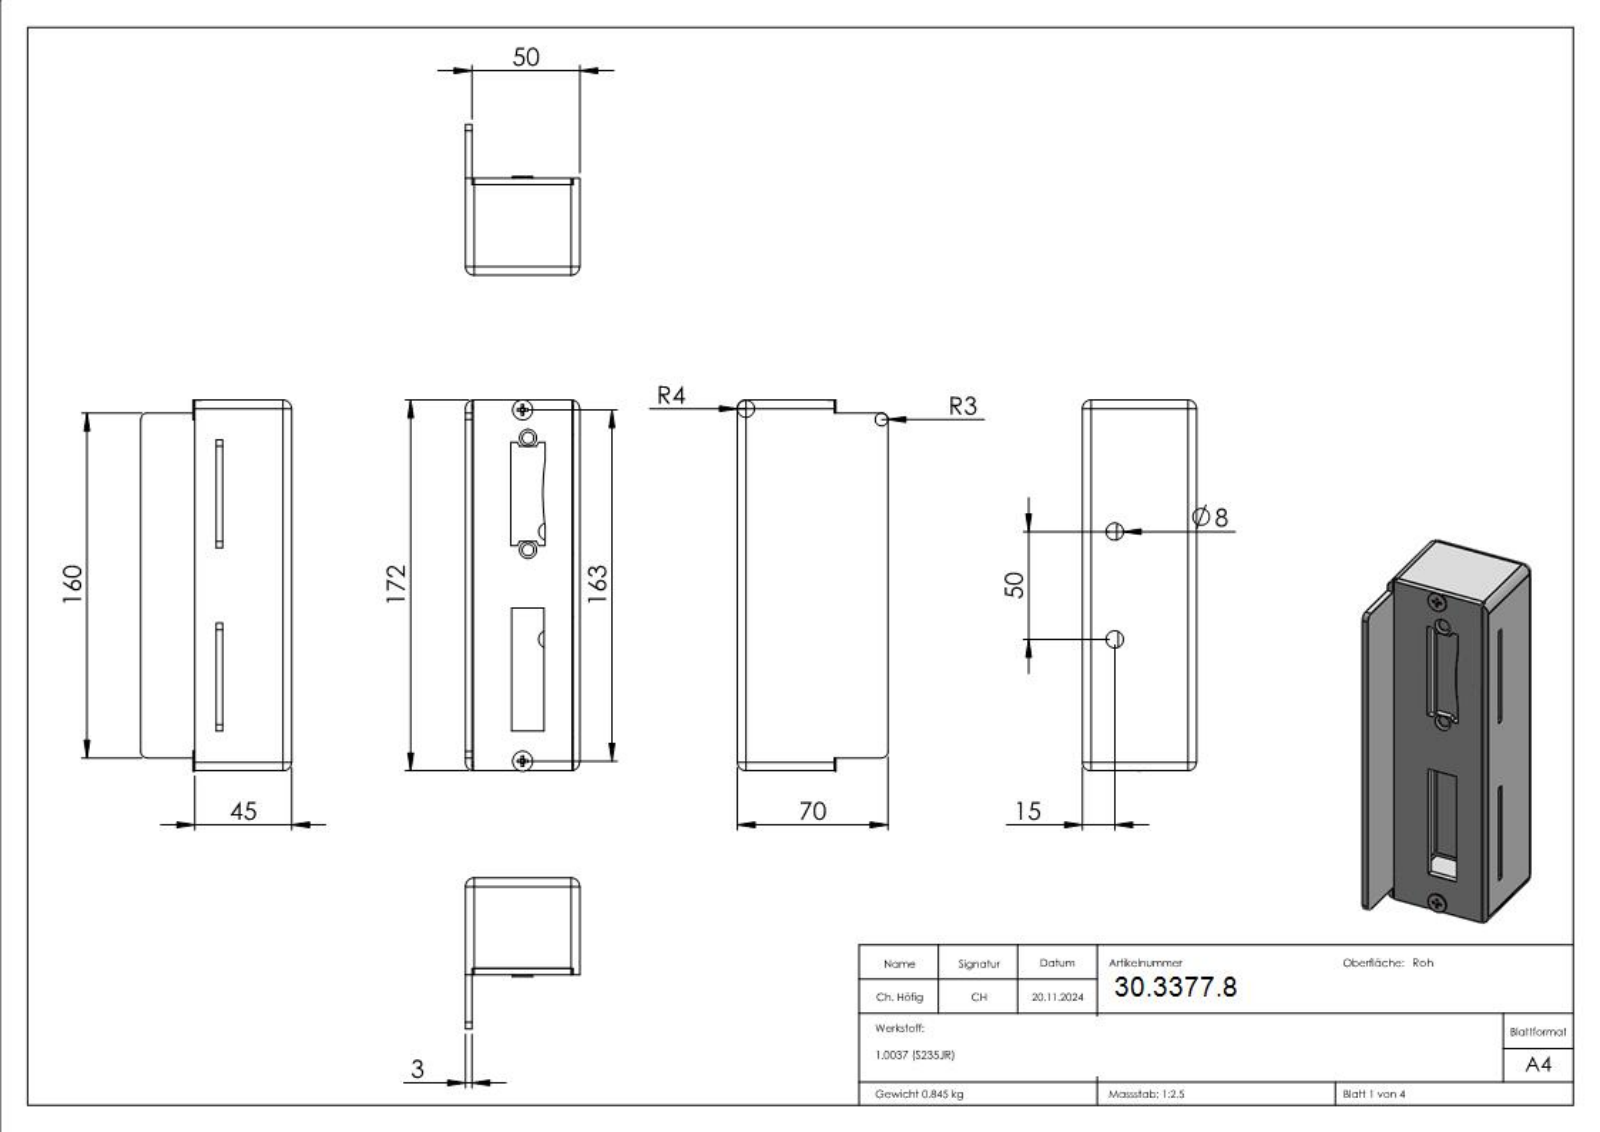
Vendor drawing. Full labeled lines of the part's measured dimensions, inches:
Part name (STEP PRODUCT): countersunk flat head cross recess screw_din_ISO 7046-1 - M5 x 10 - Z --- 10S; 591xx-ST Teil1_50mm; 591xx-ST Teil2_59112-SB; 59112-ST
STEP written by: SolidWorks 2018 (CONFIG_CONTROL_DESIGN)
Units: inches
Bodies: 4 solids, 234 faces (105 planar, 55 cylindrical, 74 other)
Overall size (bounding box): 6.783 × 2.756 × 2.087
Volume: 6.624 in³ · Surface area: 124.4 in²
Round holes (diameter × count): ⌀0.165 ×2, ⌀0.213 ×2, ⌀0.244 ×2, ⌀0.315 ×2
Round bosses / shafts (diameter × count): ⌀0.366 ×2, ⌀0.197 ×2
Partial cylindrical surfaces — rounded edges, fillets, slot ends (radius × count): R0.039 ×8, R0.157 ×8, R0.02 ×4, R0.118 ×2, R4.449 ×1
Main face-to-face distances: 0.118, 1.969, 1.654, 1.85, 1.772, 2.087, 1.535, 0.075, 6.697, 6.772
Hole centre spacings: 2.27, 4.217, 0.487, 0.521, 1.672, 1.749, 1.969, 2.047
